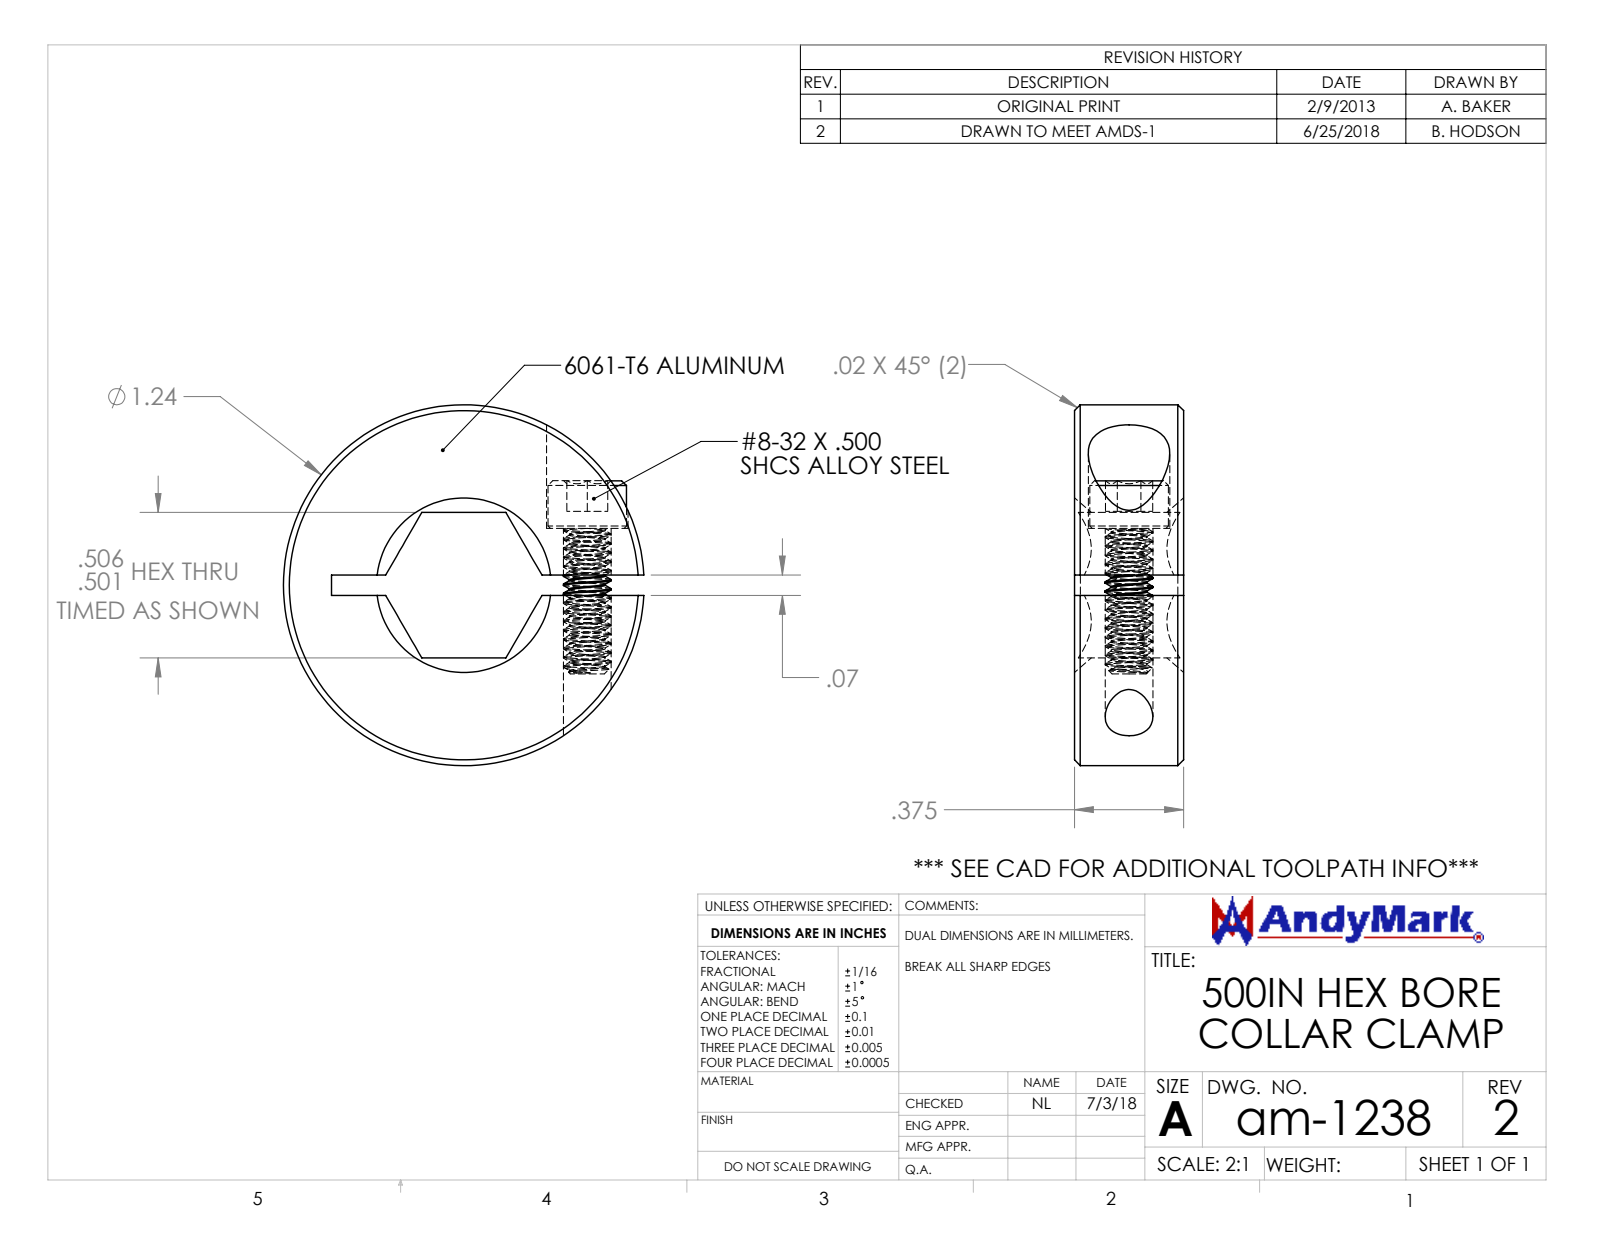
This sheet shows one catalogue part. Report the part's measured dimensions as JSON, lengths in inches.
{"part_name": "am-1238 Collar Clamp, 0.5'''''''' Hex Bore, Aluminum REV2; am-1238 Clamp Only; am-1238 Screw Only_91251A194", "step_written_by": "SolidWorks 2018 (AUTOMOTIVE_DESIGN)", "units": "inches", "bodies": {"solids": 2, "faces": 126, "planar": 24, "cylindrical": 76, "other": 26}, "overall_size": [1.24, 1.239, 0.375], "volume_in3": 0.342, "surface_area_in2": 5.252, "round_holes": [[0.28, 1]], "round_bosses_or_shafts": [[1.24, 1], [0.27, 1], [0.164, 1], [0.123, 1]], "face_to_face_distances": [0.375, 0.5, 0.07, 0.215, 0.285, 0.055, 0.16, 0.23, 0.445, 0.141]}
